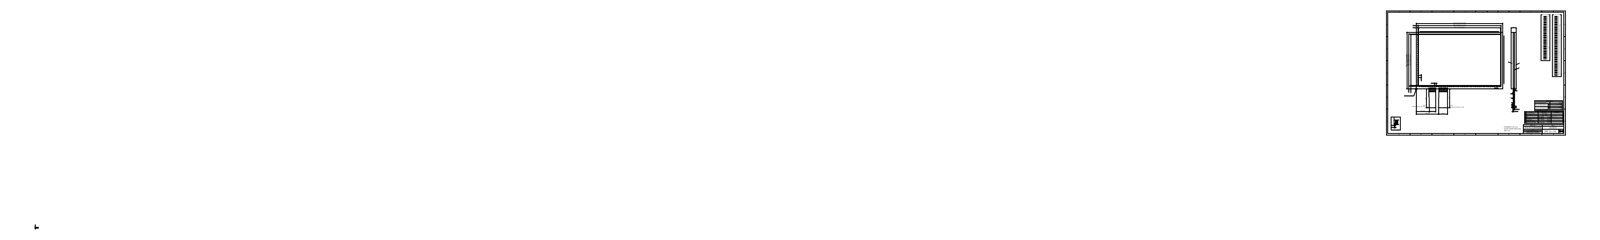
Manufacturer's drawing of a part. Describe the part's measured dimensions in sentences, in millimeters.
The part is named "DUS-N121WA060B". Its 3-D file was written by "Autodesk Inventor 2020 (AUTOMOTIVE_DESIGN)". It is 1 solid with 410 faces: 406 planar, 4 cylindrical and 0 other. Overall it measures 385 by 276 by 2.35 millimeters. Its volume is 116 739 cubic millimeters and its surface area 107 086 square millimeters. Partial cylindrical surfaces (rounded edges, fillets, slot ends): 4 of radius 0.2. The main face-to-face distances are 2.35, 1.2, 1.15, 1.25, 1.1, 180, 0.8, 1.55, 0.4, 275.
